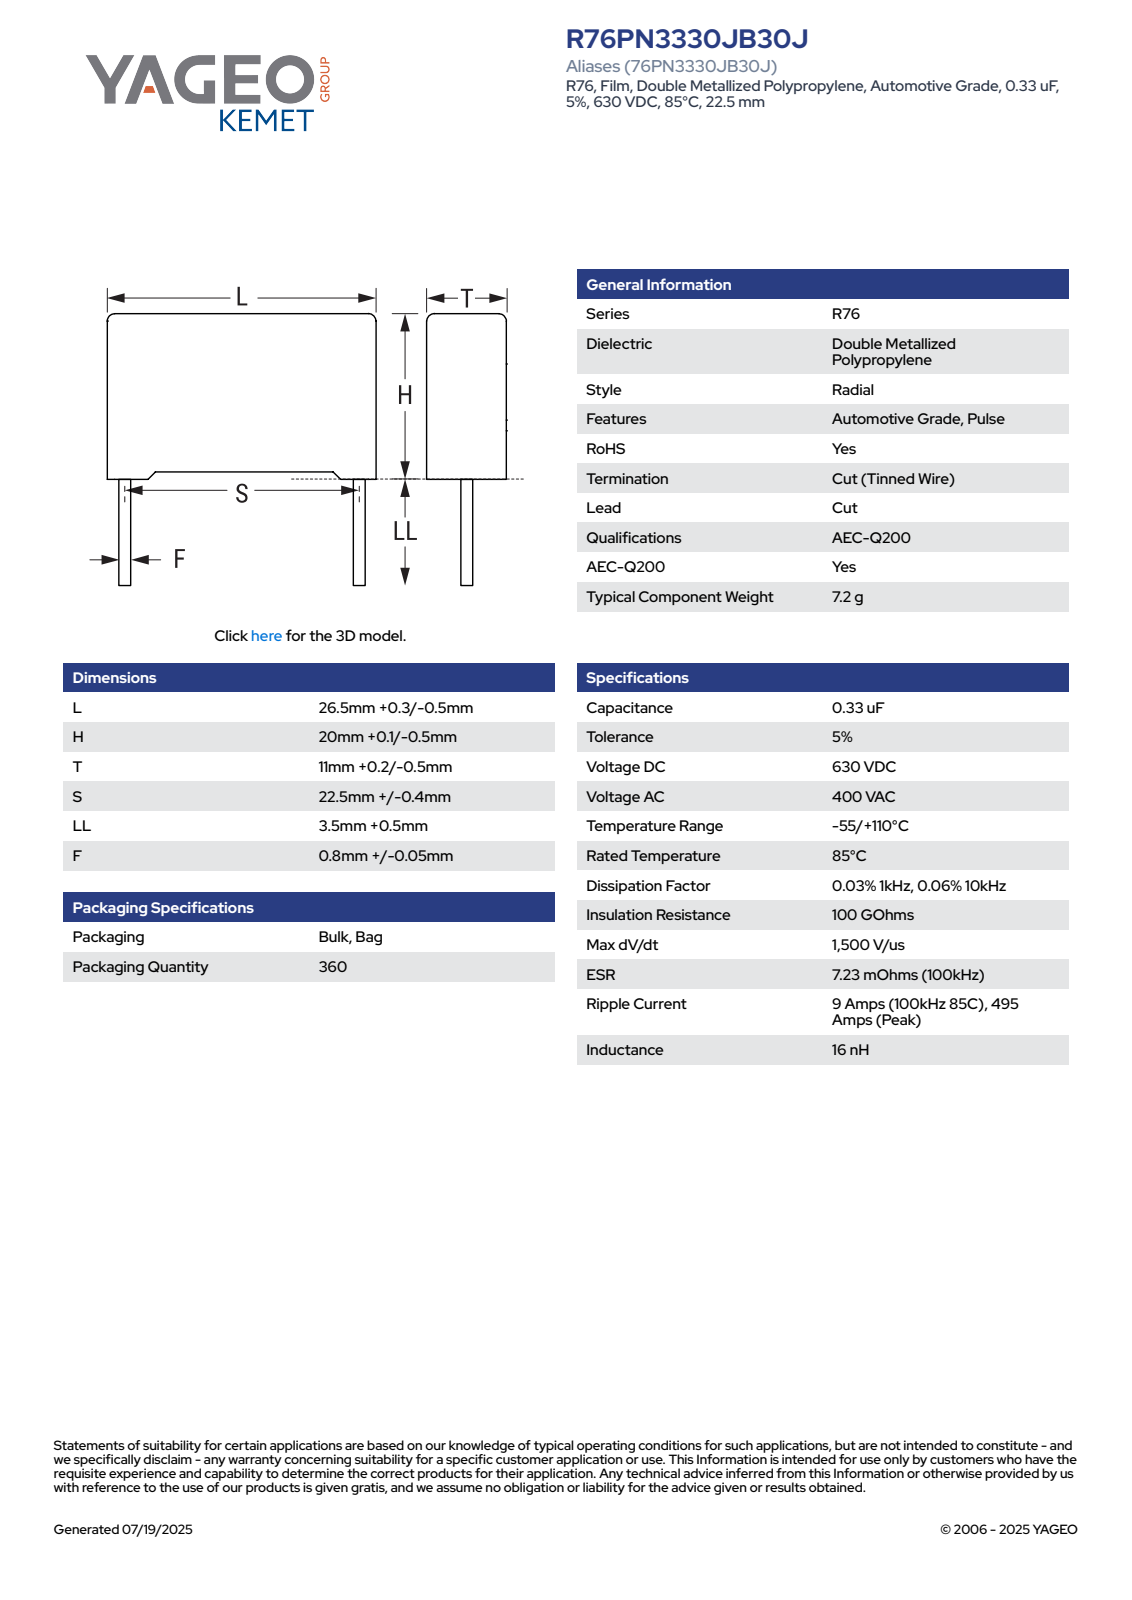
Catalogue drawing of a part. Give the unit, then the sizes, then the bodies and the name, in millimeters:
Units: millimetres
Overall size (bounding box): 26.8 × 24.1 × 11.21
Round bosses / shafts (diameter × count): ⌀0.85 ×2
Partial cylindrical surfaces — rounded edges, fillets, slot ends (radius × count): R0.5 ×4
Main face-to-face distances: 11.2, 19.35, 26.8, 19.41, 0.75, 0.69, 20.1, 0.89, 25.91, 11.21
Volume: 5 835 mm³ · Surface area: 2 191 mm²
Bodies: 4 solids, 85 faces (77 planar, 8 cylindrical, 0 other)
Part name (STEP PRODUCT): CFR_RB2_26.5X20X11_L26.8H20.1T11.2S22.5LL4F0.85
STEP written by: SolidWorks 2021 (AUTOMOTIVE_DESIGN)
